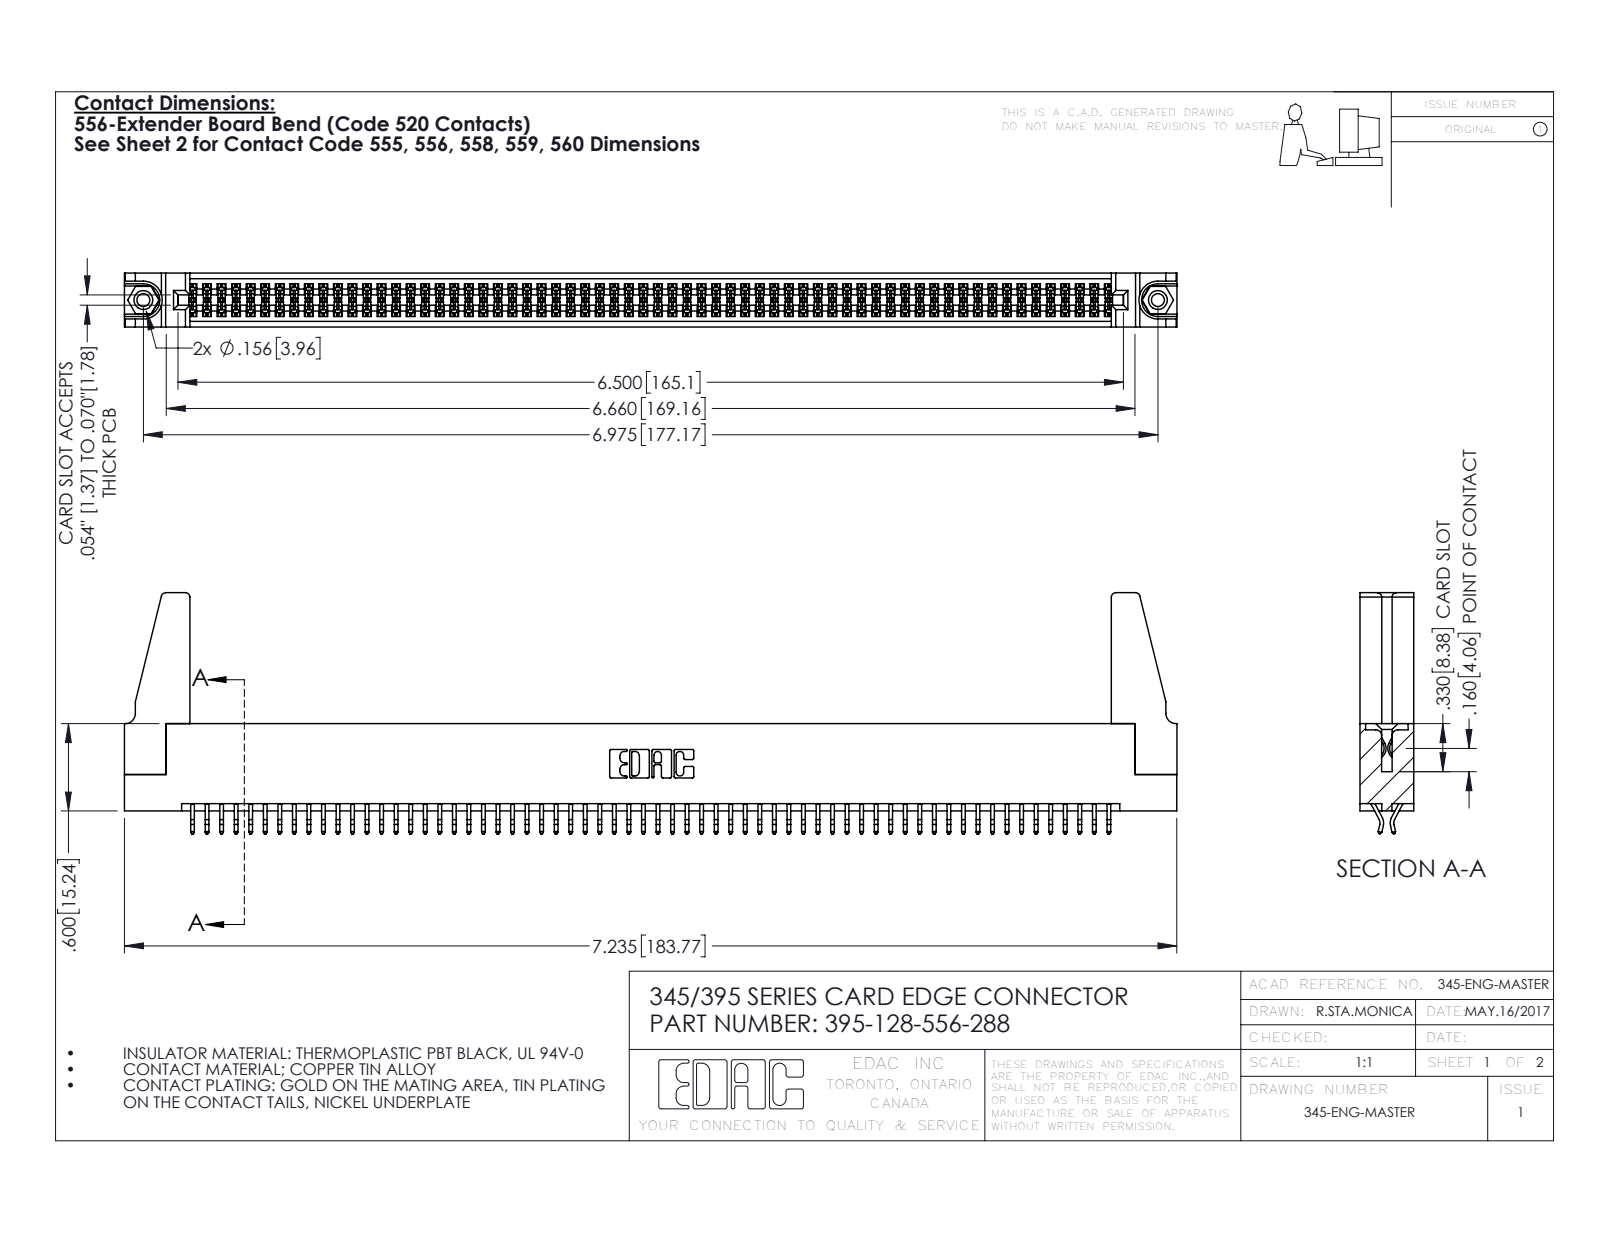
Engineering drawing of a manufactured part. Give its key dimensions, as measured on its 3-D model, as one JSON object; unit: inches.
{"part_name": "345 Part_Flush Mounting Lugs - 0.156 Dia-TH; 345-292-001_556 Tail; 395-128-556-288; 345-250-001_345-250-001-102 (+1 more)", "step_written_by": "SolidWorks 2016 (CONFIG_CONTROL_DESIGN)", "units": "inches", "bodies": {"solids": 133, "faces": 7418, "planar": 4888, "cylindrical": 2514, "other": 16}, "overall_size": [7.236, 1.657, 0.37], "volume_in3": 1.3, "surface_area_in2": 46.69, "round_holes": [[0.089, 2], [0.125, 2], [0.156, 2], [0.064, 1]], "round_bosses_or_shafts": [[0.155, 2]], "partial_cylinders_radius": [[0.006, 192], [0.01, 22], [0.03, 8], [0.007, 6], [0.031, 6], [0.026, 3], [0.01, 2], [0.014, 2]], "face_to_face_distances": [0.072, 0.298, 0.37, 0.2, 0.025, 0.098, 0.272, 0.225, 0.175, 0.149], "hole_center_spacings": [0.27, 6.739, 6.975]}
